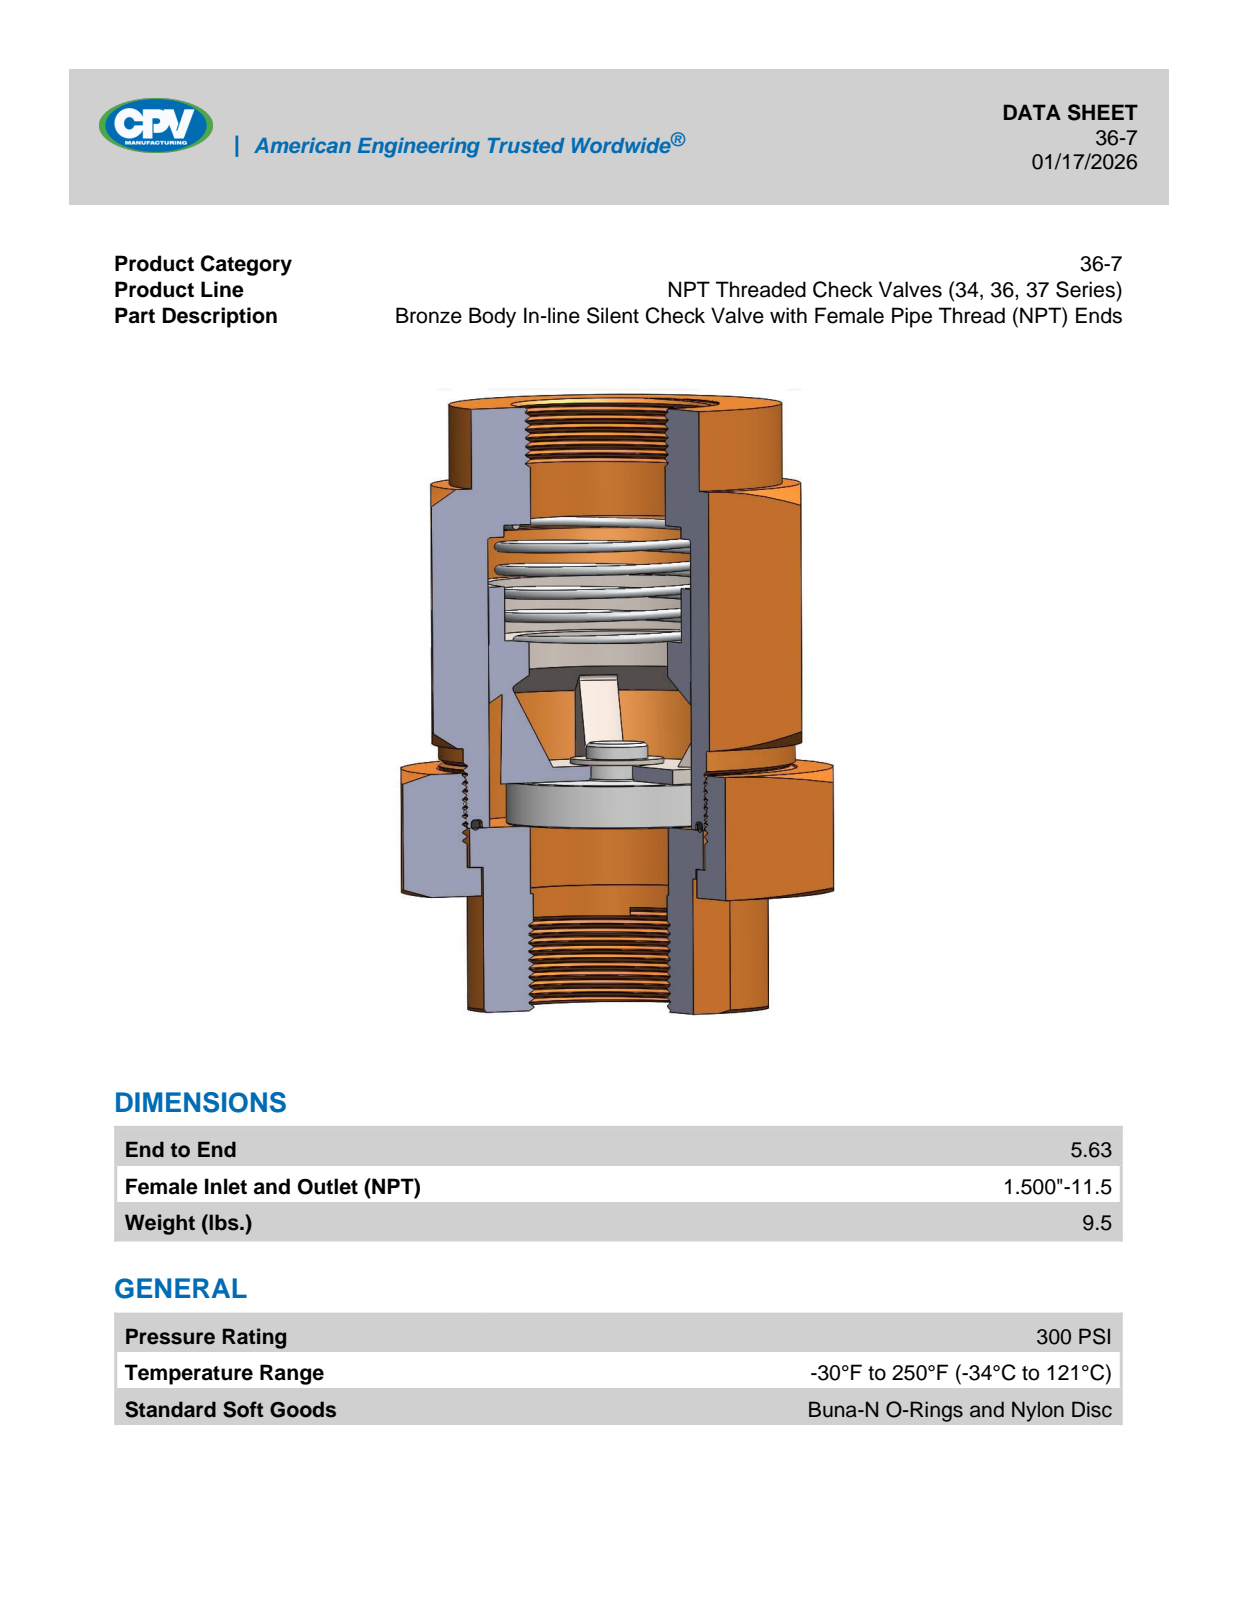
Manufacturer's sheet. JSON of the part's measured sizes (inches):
{"part_name": "36-7", "step_written_by": "SolidWorks 2018 (AUTOMOTIVE_DESIGN)", "units": "inches", "bodies": {"solids": 1, "faces": 113, "planar": 28, "cylindrical": 44, "other": 41}, "overall_size": [5.56, 4.261, 3.69], "volume_in3": 40.93, "surface_area_in2": 98.27, "round_holes": [[1.5, 1]], "round_bosses_or_shafts": [[2.995, 1], [2.75, 1]], "partial_cylinders_radius": [[1.305, 1]], "face_to_face_distances": [0.28, 3.41, 3.13, 3.69, 0.6, 3.09, 0.32, 2.81, 4.45, 1.19]}
